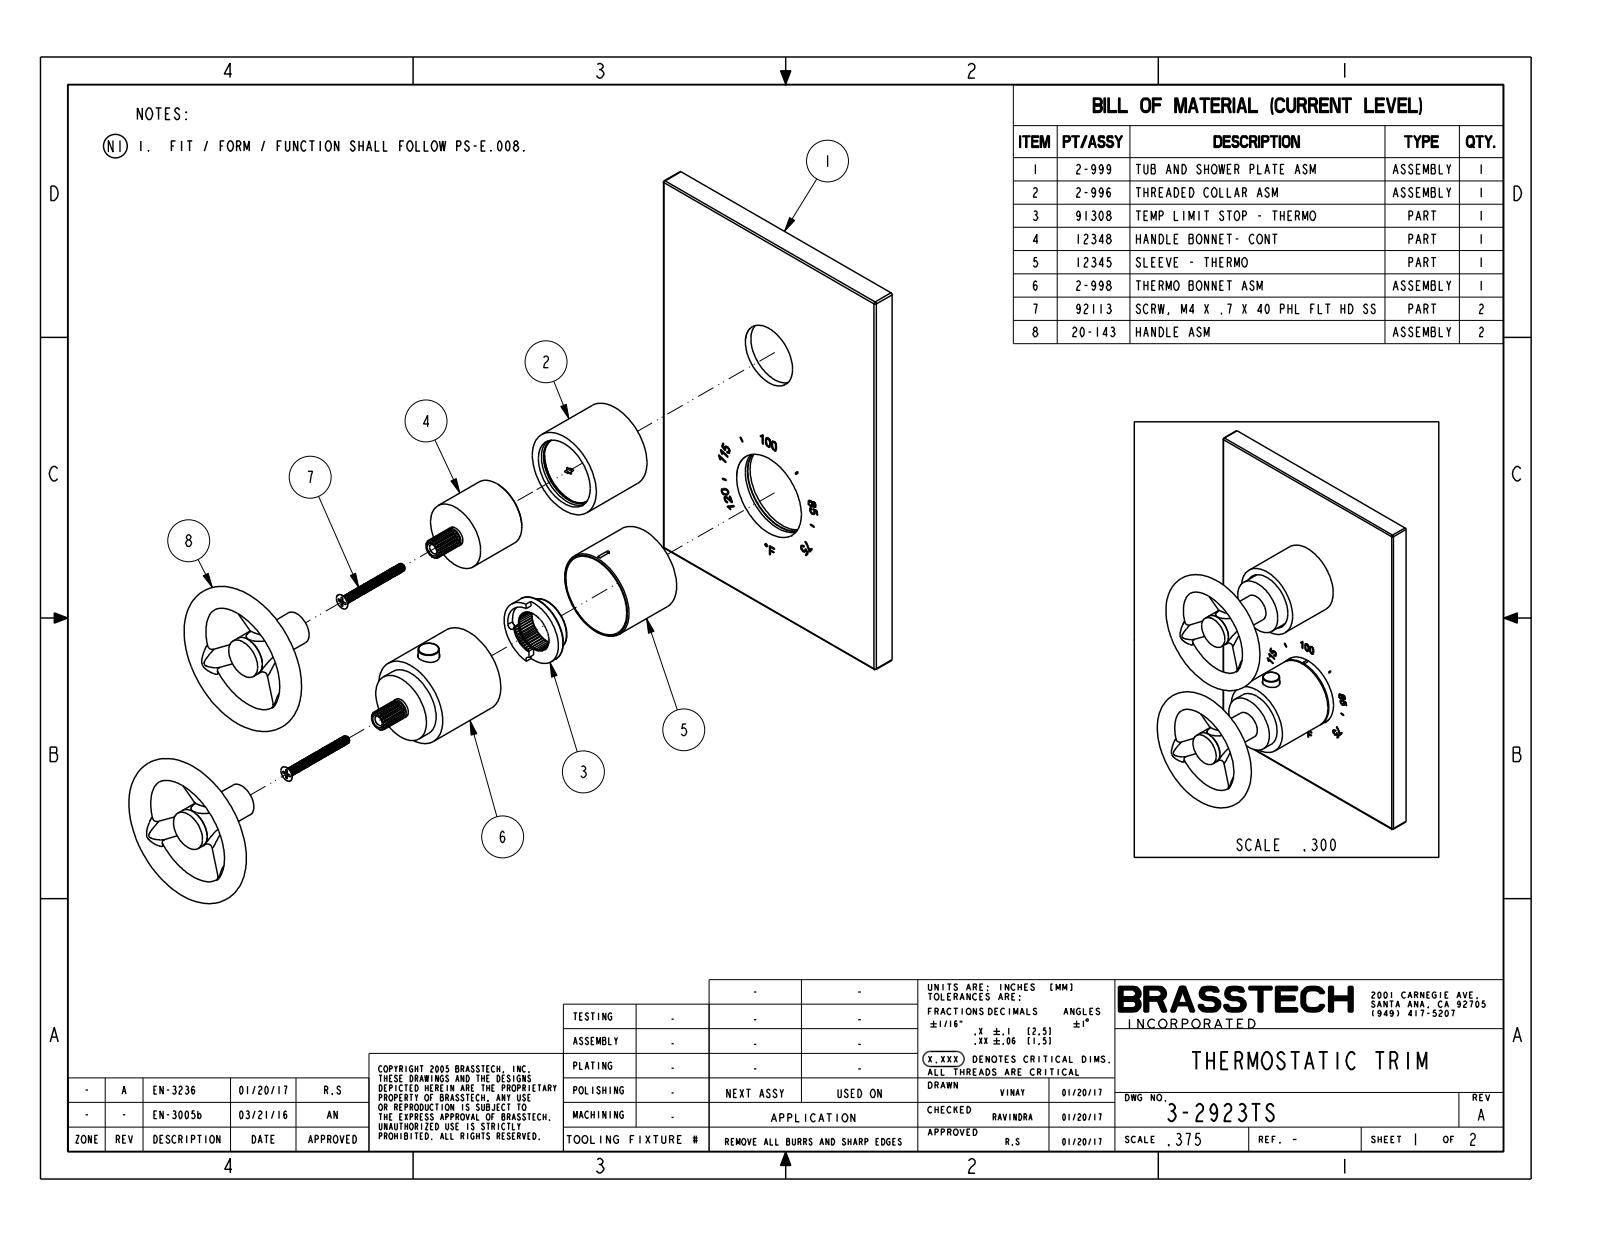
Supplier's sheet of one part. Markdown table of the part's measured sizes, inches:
| quantity | value |
| --- | --- |
| part name | 12349; 91678; 2-999_ASM; 12368 (+8 more) |
| STEP written by | PRO/ENGINEER BY PARAMETRIC TECHNOLOGY CORPORATION, 2014000 (CONFIG_CONTROL_DESIGN) |
| units | inches |
| bodies | 21 solids, 1745 faces (633 planar, 565 cylindrical, 547 other) |
| overall size | 8.25 × 5.5 × 3.981 |
| volume | 12.1 in³ |
| surface area | 216.9 in² |
| round holes (diameter × count) | 0.188 × 2, 0.19 × 2, 0.265 × 2, 0.276 × 2, 0.358 × 2, 0.4 × 2, 0.422 × 2, 0.51 × 2, 0.063 × 1, 0.079 × 1, 0.1 × 1, 0.126 × 1 |
| round bosses / shafts (diameter × count) | 0.35 × 6, 0.157 × 3, 1.654 × 2, 0.75 × 2, 0.63 × 2, 0.512 × 2, 0.51 × 2, 0.49 × 2 |
| partial cylindrical surfaces (radius × count) | 0.03 × 8, 0.5 × 8, 0.039 × 2, 0.075 × 2, 0.082 × 2, 0.125 × 2, 0.164 × 2, 0.169 × 2 |
| main face-to-face distances | 0.08, 0.168, 0.248, 0.08, 0.25, 0.33, 5.5, 5.42, 0.19, 0.358 |
| hole center spacings | 0.554, 1.144, 1.696, 2.596, 2.596, 3.15, 3.15, 4.292 |
